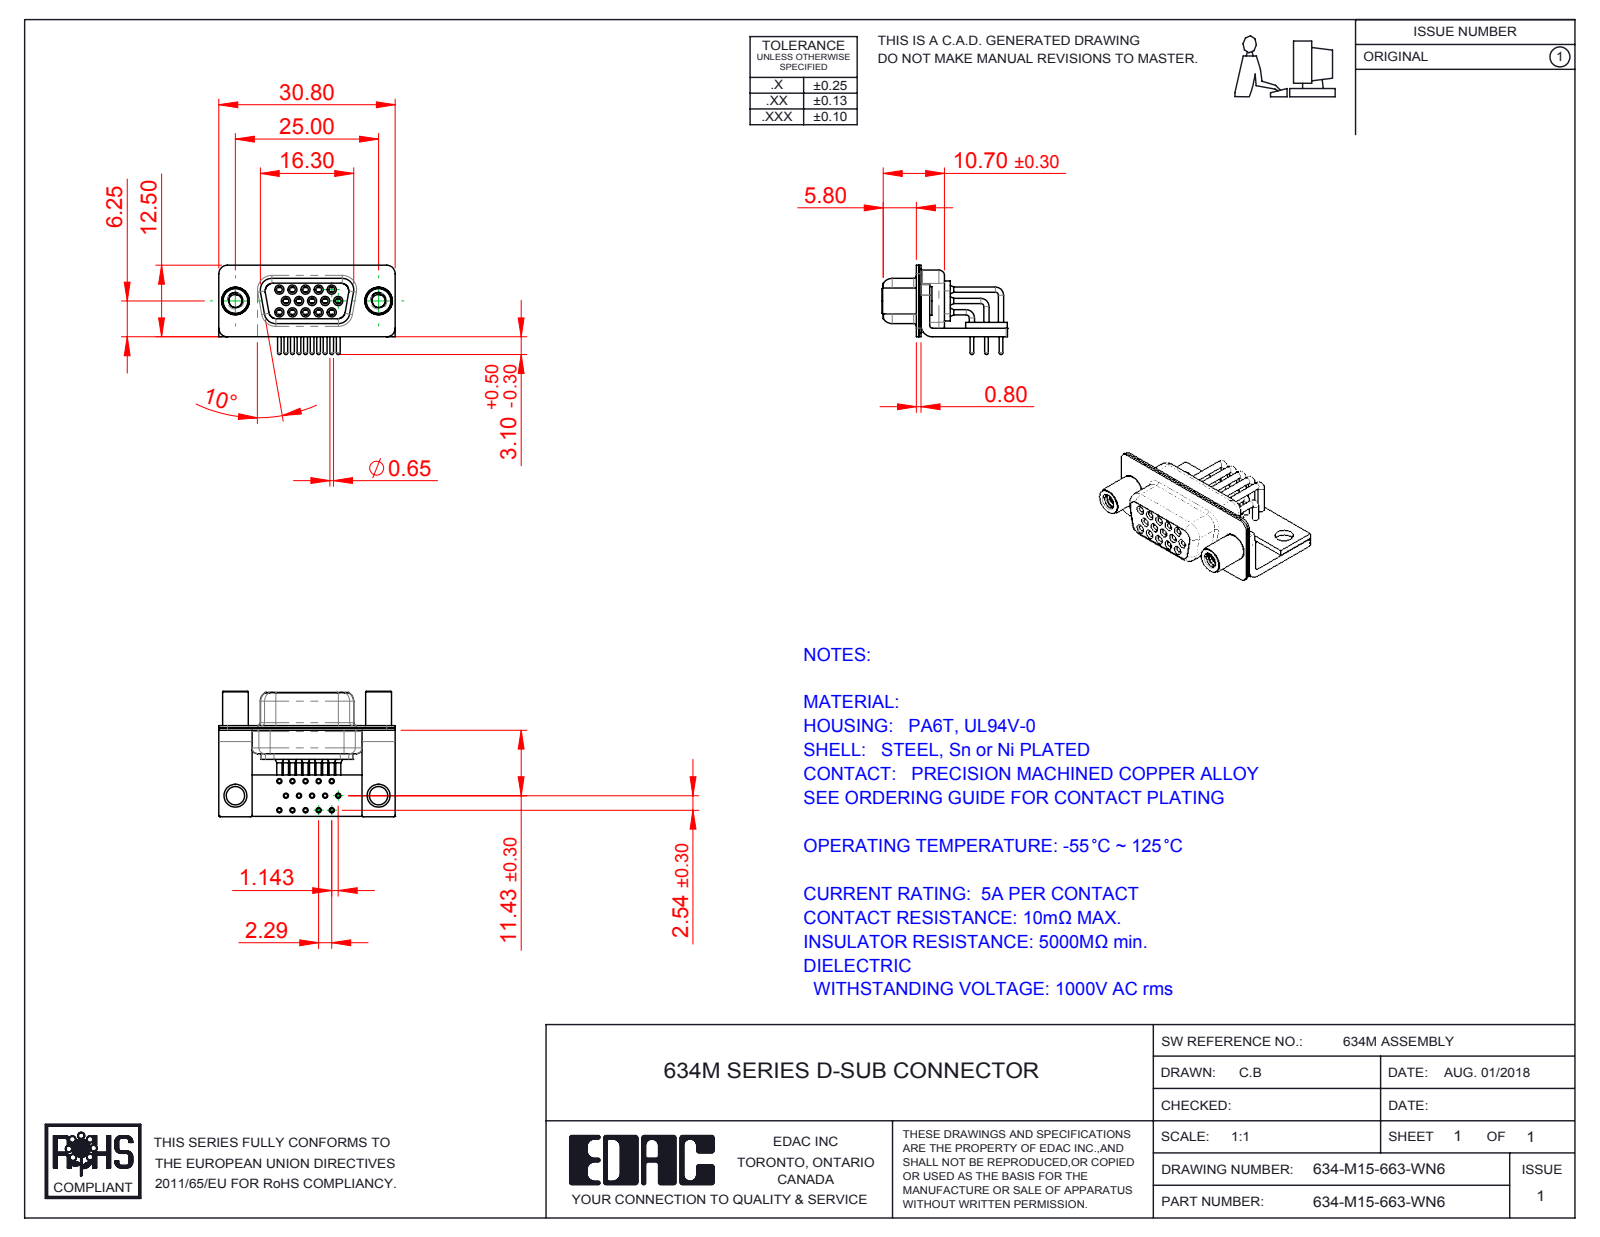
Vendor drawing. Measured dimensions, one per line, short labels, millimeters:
name: 634M Contact Row 1; 634M Shell Rear_15 Contacts; 634M Shell Front_15 Contacts; 634-M15-663-WN6 (+6 more)
written by: SolidWorks 2016 (CONFIG_CONTROL_DESIGN)
unit: mm
bodies: 23 solids, 1204 faces (320 planar, 576 cylindrical, 308 other)
size: 30.8 × 21.9 × 15.6
volume: 2 343 mm³; area: 7 138 mm²
holes: 15× ⌀0.9, 15× ⌀1, 15× ⌀1.1, 15× ⌀1.7, 15× ⌀1.8, 15× ⌀2, 2× ⌀2.26, 2× ⌀3.2, 2× ⌀4, 2× ⌀4.8
bosses: 15× ⌀1.6, 15× ⌀1.5, 15× ⌀0.9, 15× ⌀0.65, 2× ⌀5, 2× ⌀4.9, 2× ⌀4.5, 1× ⌀2
rounds: 16× R0.25, 16× R1.5, 13× R2, 8× R1.35, 8× R1.6, 5× R0.5, 4× R0.6, 4× R0.65
face distances: 0.4, 1.5, 0.8, 2.3, 1.9, 1, 9.35, 8.5, 1.45, 0.85
hole spacings: 2.29, 2.28, 4.57, 3.96, 4.27, 2.78, 6.05, 6.86
